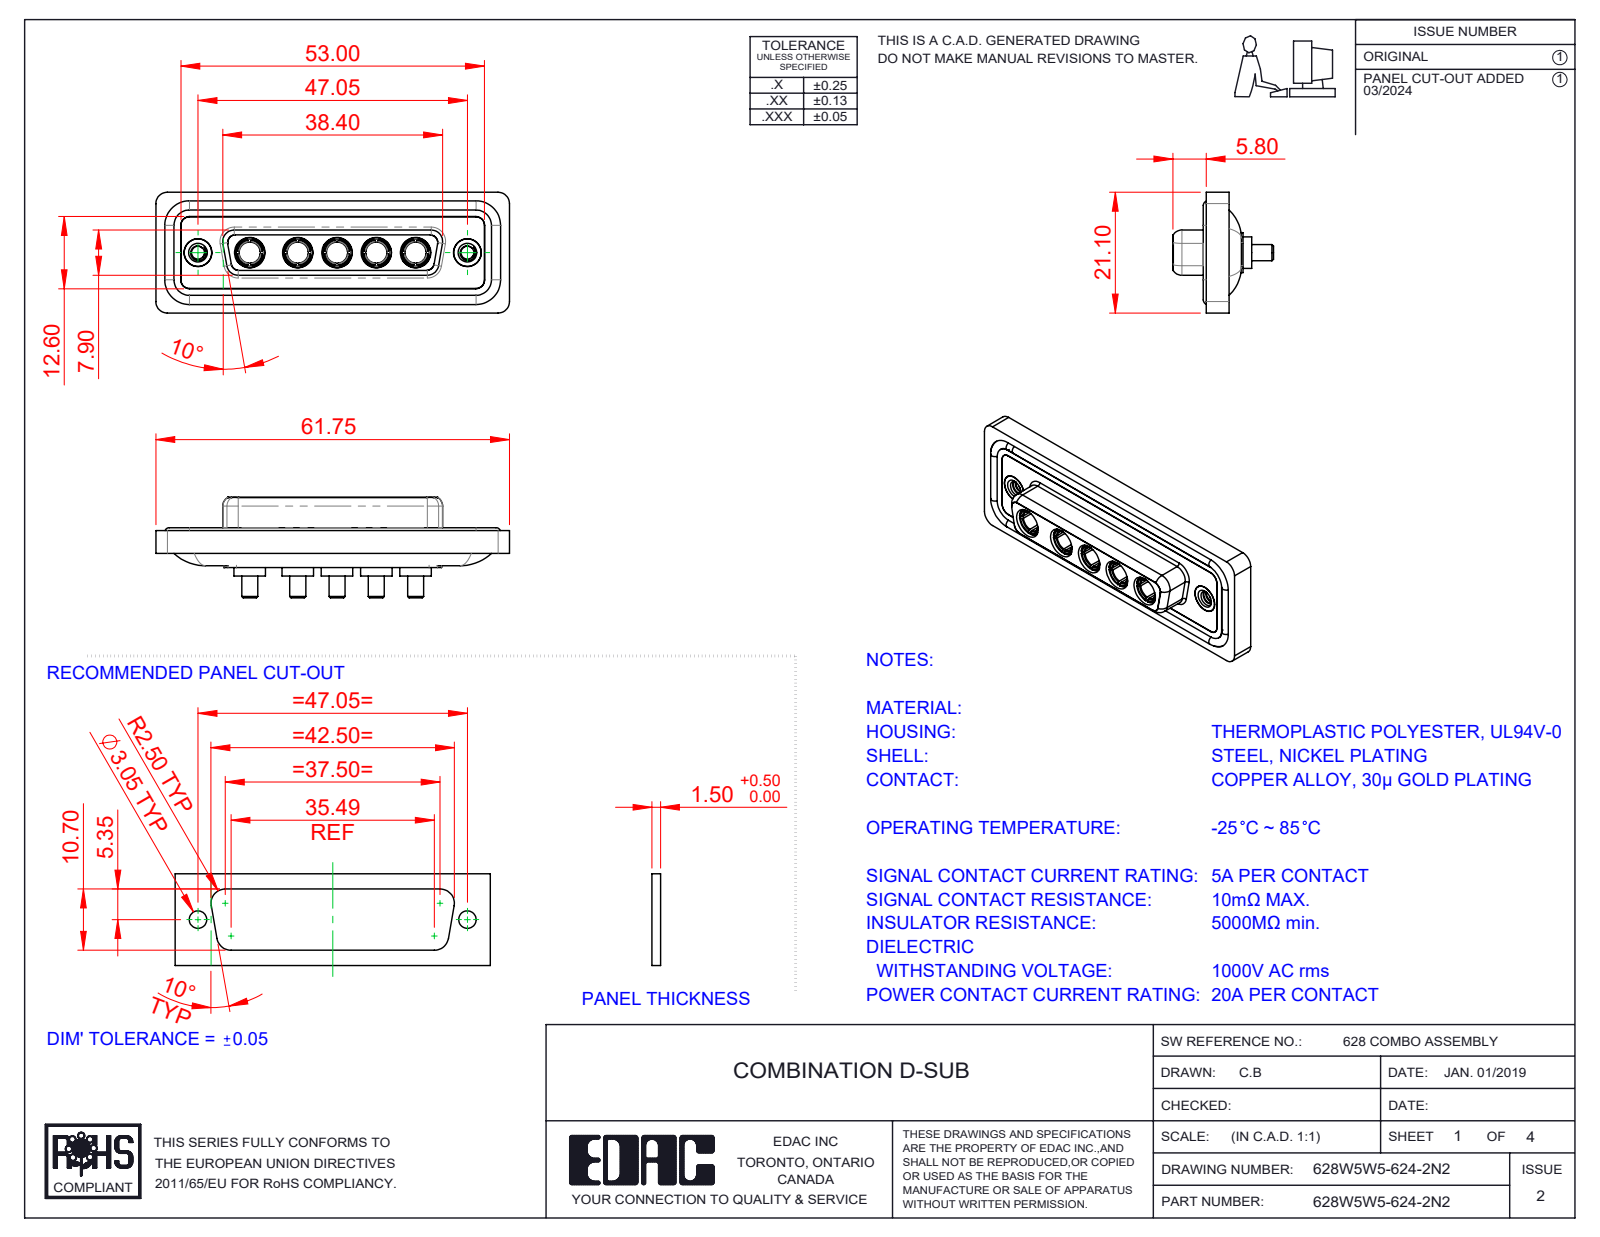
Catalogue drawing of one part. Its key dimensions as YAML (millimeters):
part_name: "628Combo Shell Front_25 Contacts; 628Combo Shell Rear_25 Contacts; 628W5W5-624-2N2; 628Combo Threaded Rivet_2 (+3 more)"
step_written_by: "SolidWorks 2023 (CONFIG_CONTROL_DESIGN)"
units: millimeters
bodies: {solids: 17, faces: 756, planar: 250, cylindrical: 303, other: 203}
overall_size: [61.75, 21.1, 17.55]
volume: 8172
surface_area: 13415
round_holes:
  - {diameter: 4.85, count: 7}
  - {diameter: 3.7, count: 5}
  - {diameter: 5.3, count: 5}
  - {diameter: 2.26, count: 2}
  - {diameter: 4, count: 2}
  - {diameter: 4.05, count: 2}
  - {diameter: 5, count: 2}
round_bosses_or_shafts:
  - {diameter: 5.5, count: 5}
  - {diameter: 5.2, count: 5}
  - {diameter: 4.96, count: 5}
  - {diameter: 4.75, count: 5}
  - {diameter: 3.75, count: 5}
  - {diameter: 2.8, count: 5}
  - {diameter: 1.6, count: 4}
  - {diameter: 4.95, count: 2}
partial_cylinders:
  - {radius: 1.5, count: 22}
  - {radius: 2, count: 18}
  - {radius: 1.35, count: 8}
  - {radius: 1.6, count: 8}
  - {radius: 2.1, count: 5}
  - {radius: 0.25, count: 4}
  - {radius: 0.5, count: 4}
  - {radius: 0.6, count: 4}
face_to_face_distances: [0.4, 1.8, 7.45, 5.65, 0.5, 7.05, 6.6, 1.6, 1.1, 2.9]
hole_center_spacings: [6.86, 9.04, 13.72, 38.01, 8.39, 15.25, 15.9, 17.43]
